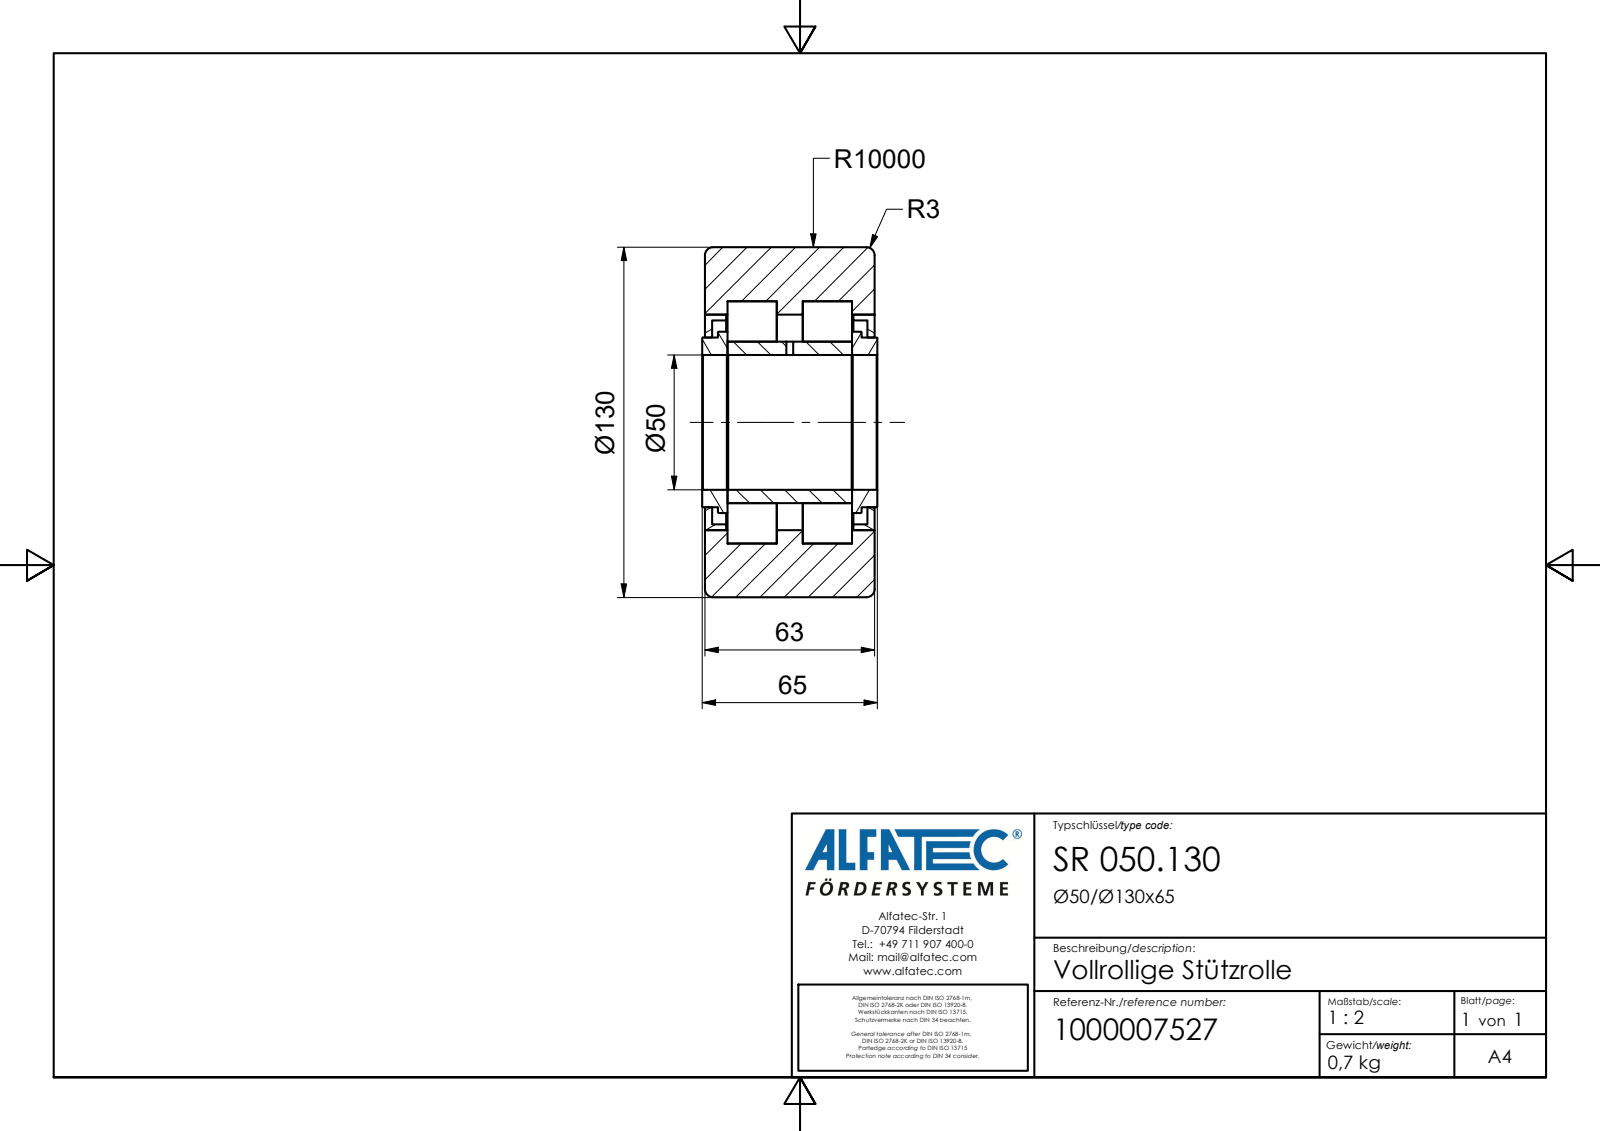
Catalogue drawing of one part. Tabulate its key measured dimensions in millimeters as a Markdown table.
| quantity | value |
| --- | --- |
| part name | SR 050.130_Kontur |
| STEP written by | Autodesk Inventor 2020 (AUTOMOTIVE_DESIGN) |
| units | millimeters |
| bodies | 1 solid, 158 faces (36 planar, 61 cylindrical, 61 other) |
| overall size | 130 × 130 × 65 |
| volume | 606 909 mm³ |
| surface area | 113 900 mm² |
| round holes (diameter × count) | 2.5 × 1, 50 × 1, 75.75 × 1, 80 × 1, 90 × 1 |
| round bosses / shafts (diameter × count) | 15 × 9, 67.33 × 1, 63 × 1, 60 × 1 |
| main face-to-face distances | 63, 27.92, 2.62, 60.38, 26.7, 36.3, 24.08, 33.68, 8.38, 54.62 |
